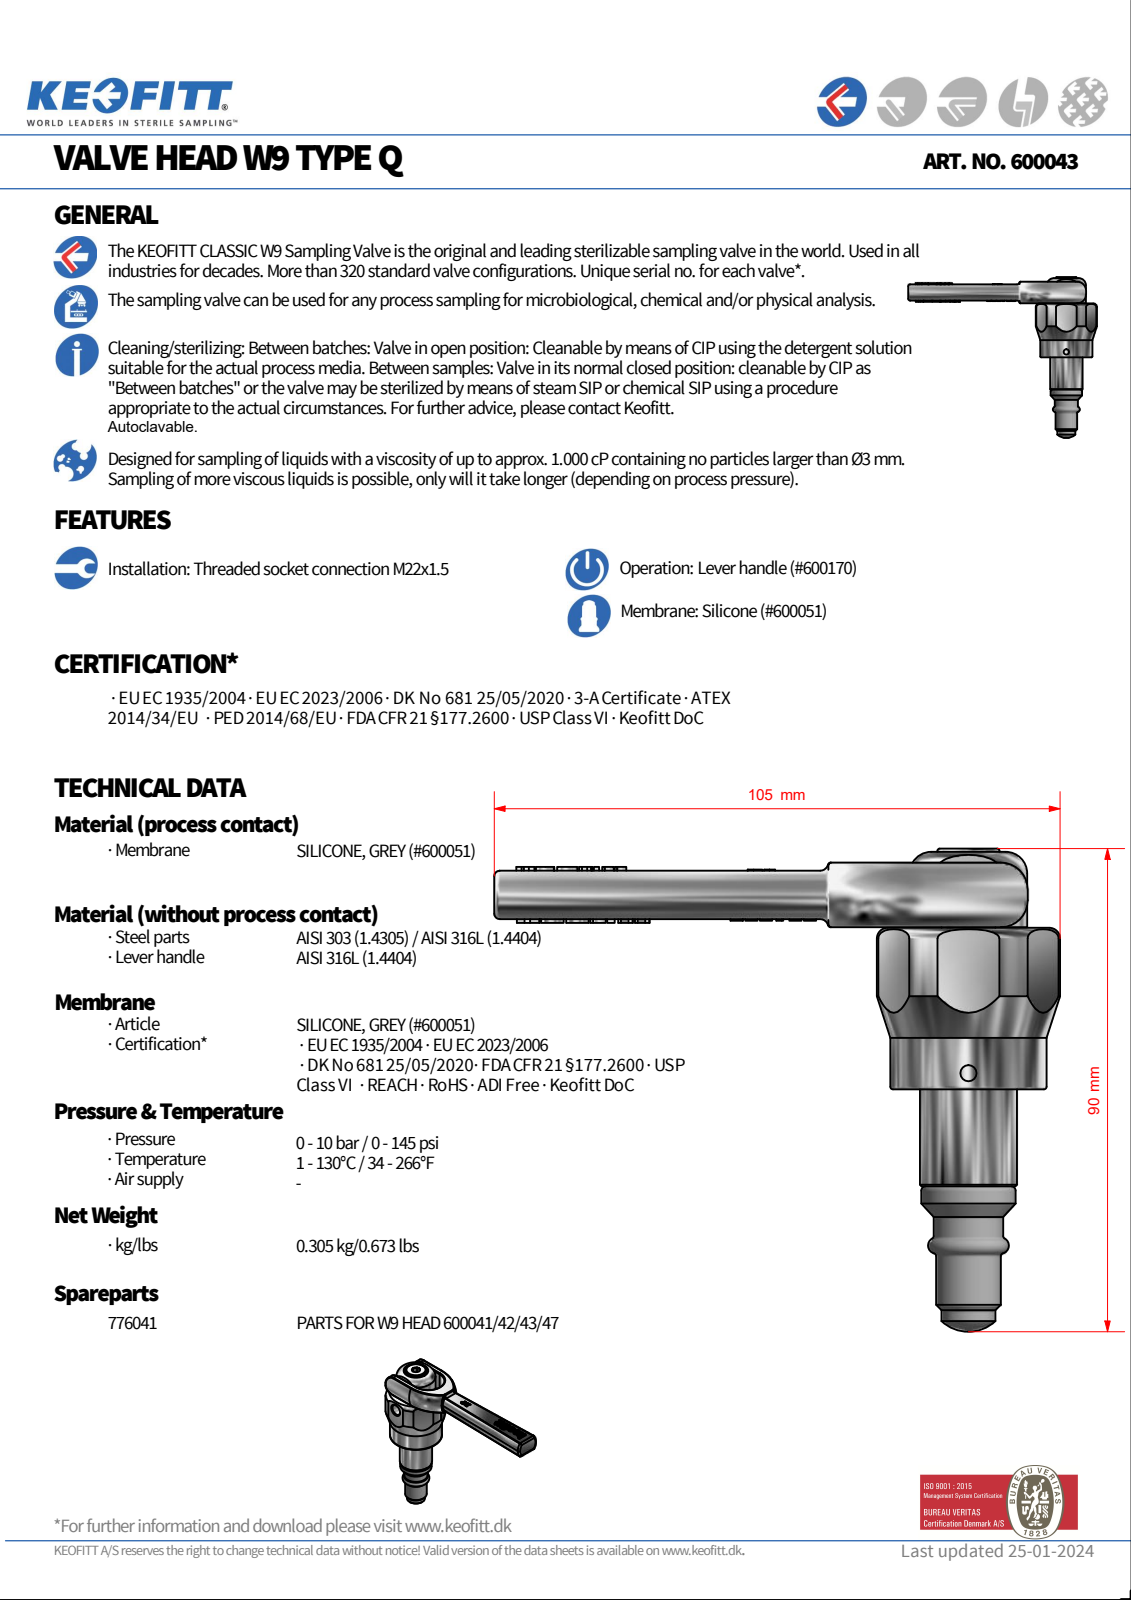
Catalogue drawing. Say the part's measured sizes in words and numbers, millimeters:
Its 3-D file was written by "Autodesk Inventor 2008 (AUTOMOTIVE_DESIGN)". It is 1 solid with 555 faces: 234 planar, 64 cylindrical and 257 other. Overall it measures 104.83 by 89.1 by 32 millimeters. Its volume is 45 608 cubic millimeters and its surface area 14 587 square millimeters. Round holes: 1 of diameter 2.5, 1 of diameter 3.05, 1 of diameter 6, 1 of diameter 6.05, 1 of diameter 8.4, 1 of diameter 10.1, 1 of diameter 11.5, 1 of diameter 23.4. Round bosses or shafts: 1 of diameter 29, 1 of diameter 18, 1 of diameter 17.5, 1 of diameter 14, 1 of diameter 12.9, 1 of diameter 12, 1 of diameter 10, 1 of diameter 7.6. Partial cylindrical surfaces (rounded edges, fillets, slot ends): 14 of radius 0.5, 4 of radius 1.5, 2 of radius 1, 2 of radius 5, 1 of radius 3, 1 of radius 5.4, 1 of radius 9.1, 1 of radius 11. The main face-to-face distances are 1.5, 10.5, 10.6, 1.6, 32, 9, 12, 12.1, 30, 30.1. The hole center spacings are 2, 9.14, 11.13, 22, 24, 33.11.
